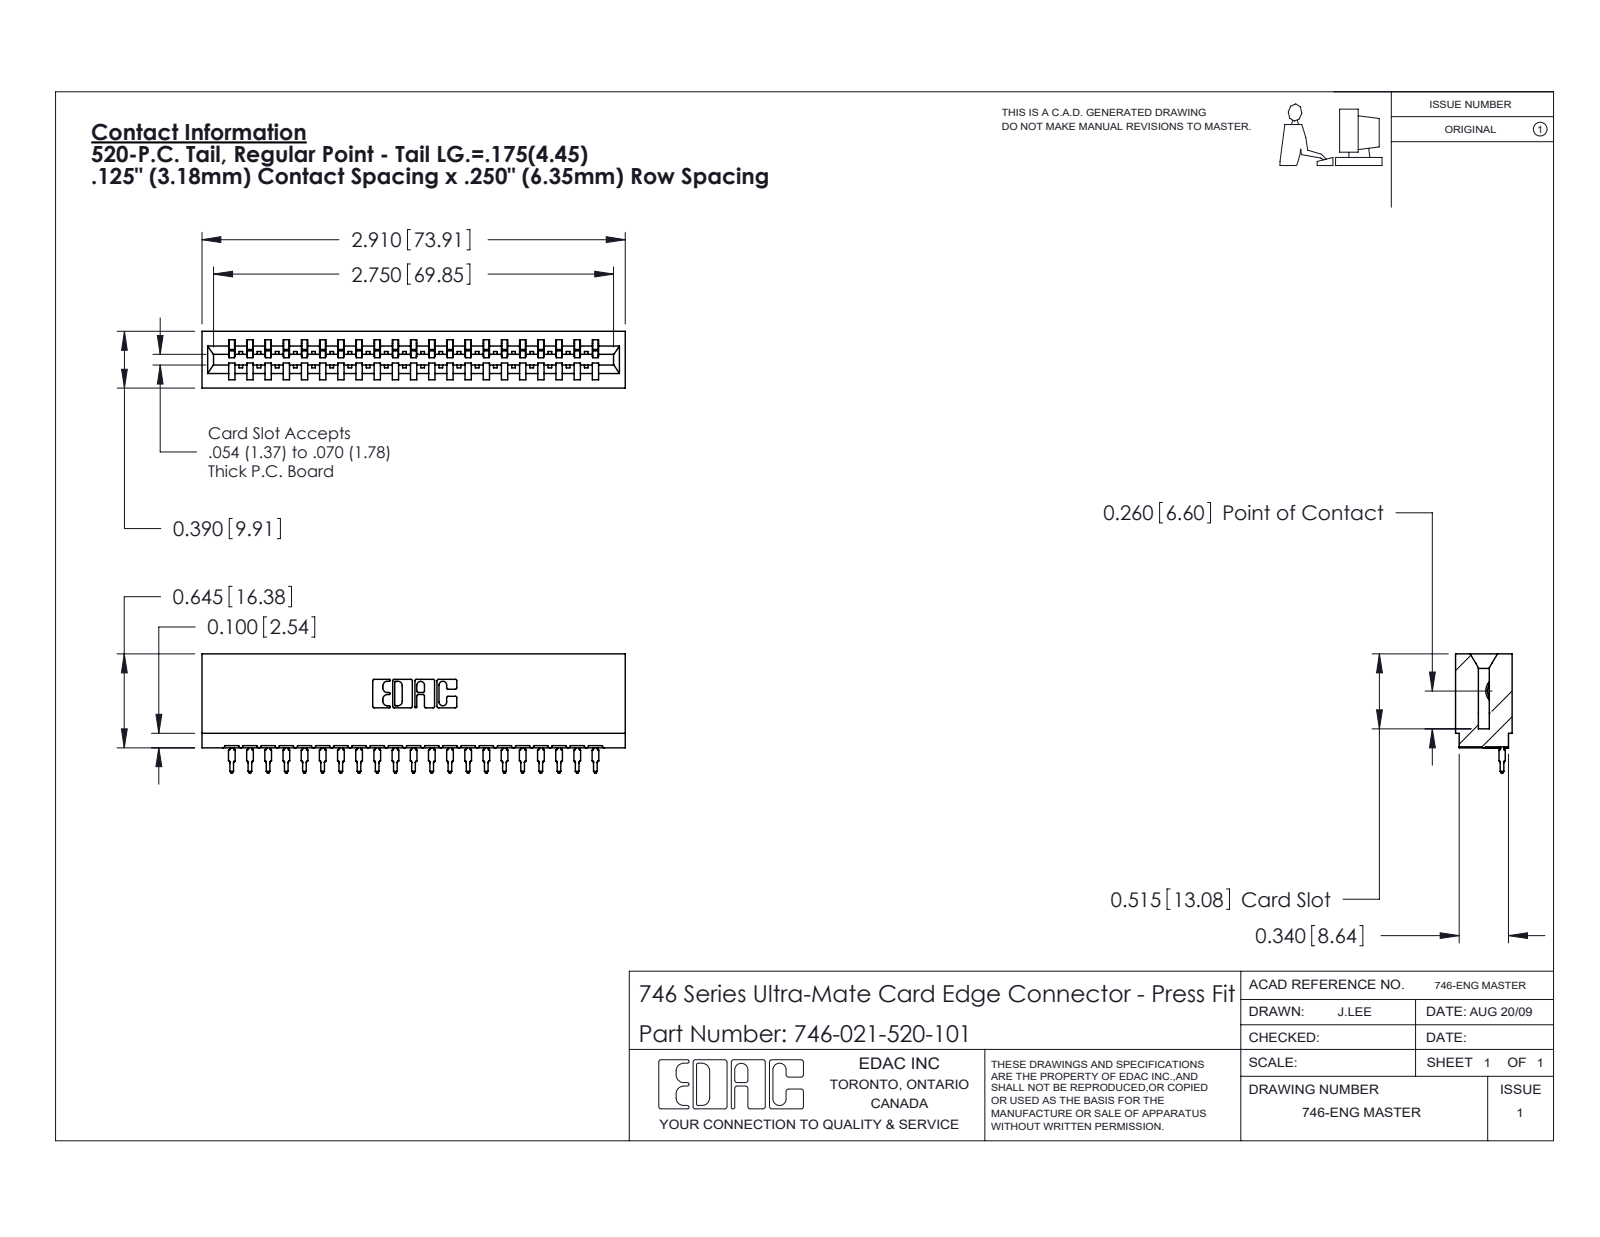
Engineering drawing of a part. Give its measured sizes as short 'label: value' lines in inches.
name: 746 Part_.515 Slot Depth - 01; 746-292-001_520; 746-021-520-101
written by: SolidWorks 2020 (CONFIG_CONTROL_DESIGN)
unit: in
bodies: 22 solids, 2365 faces (1378 planar, 441 cylindrical, 546 other)
size: 2.91 × 0.819 × 0.39
volume: 0.478 in³; area: 17.23 in²
rounds: 42× R0.021, 22× R0.01, 22× R0.015, 6× R0.007, 6× R0.031, 4× R0.005, 4× R0.011, 3× R0.026
face distances: 0.25, 0.333, 0.057, 0.39, 0.5, 0.042, 0.125, 0.025, 0.307, 0.375
